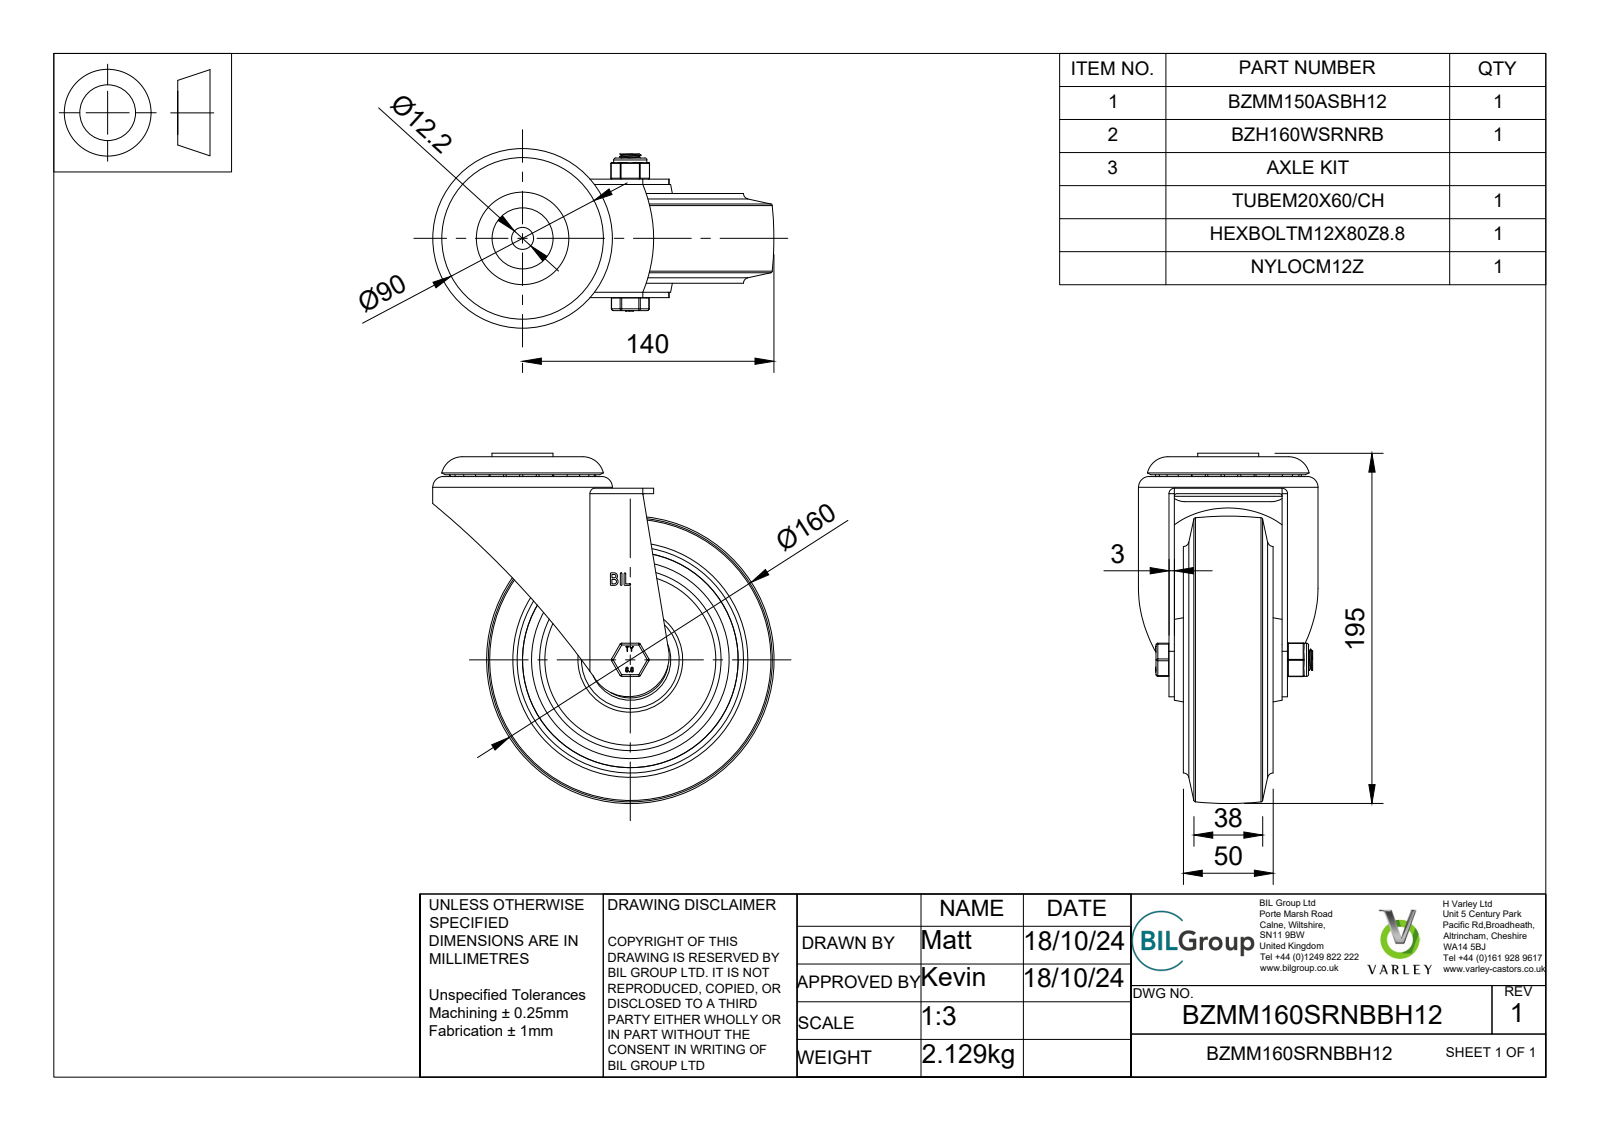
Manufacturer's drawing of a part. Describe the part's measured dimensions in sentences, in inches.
The part is named "BZMM160SRNBBH12 v3; BZMM150ASBH12 v1; ZINC PLATED, PRESSED STEEL FORKS; ZINC PLATED, PRESSED STEEL HEAD (+6 more)". Its 3-D file was written by "Autodesk Translation Framework v13.20.0.188 (AUTOMOTIVE_DESIGN)". It is 62 solids with 457 faces: 178 planar, 130 cylindrical and 149 other. Overall it measures 7.677 by 7.48 by 3.937 inches. Its volume is 48.89 cubic inches and its surface area 373.1 square inches. Round holes: 1 of diameter 0.472, 1 of diameter 0.48, 1 of diameter 0.492, 1 of diameter 0.551, 1 of diameter 0.787, 1 of diameter 1.181, 1 of diameter 1.535, 1 of diameter 1.575, 1 of diameter 2.283, 1 of diameter 3.701, 1 of diameter 4.724. Round bosses or shafts: 8 of diameter 0.197, 1 of diameter 3.937, 1 of diameter 2.48, 1 of diameter 1.339, 1 of diameter 0.945, 1 of diameter 0.783, 1 of diameter 0.728, 1 of diameter 0.709. Partial cylindrical surfaces (rounded edges, fillets, slot ends): 18 of radius 0.02, 12 of radius 0.039, 4 of radius 0.059, 2 of radius 0.118, 1 of radius 0.531, 1 of radius 0.888, 1 of radius 3.071, 1 of radius 19.782. The main face-to-face distances are 0.118, 1.063, 1.299, 1.181, 1.417, 2.48, 0.315, 0.236, 0.197, 0.866.
